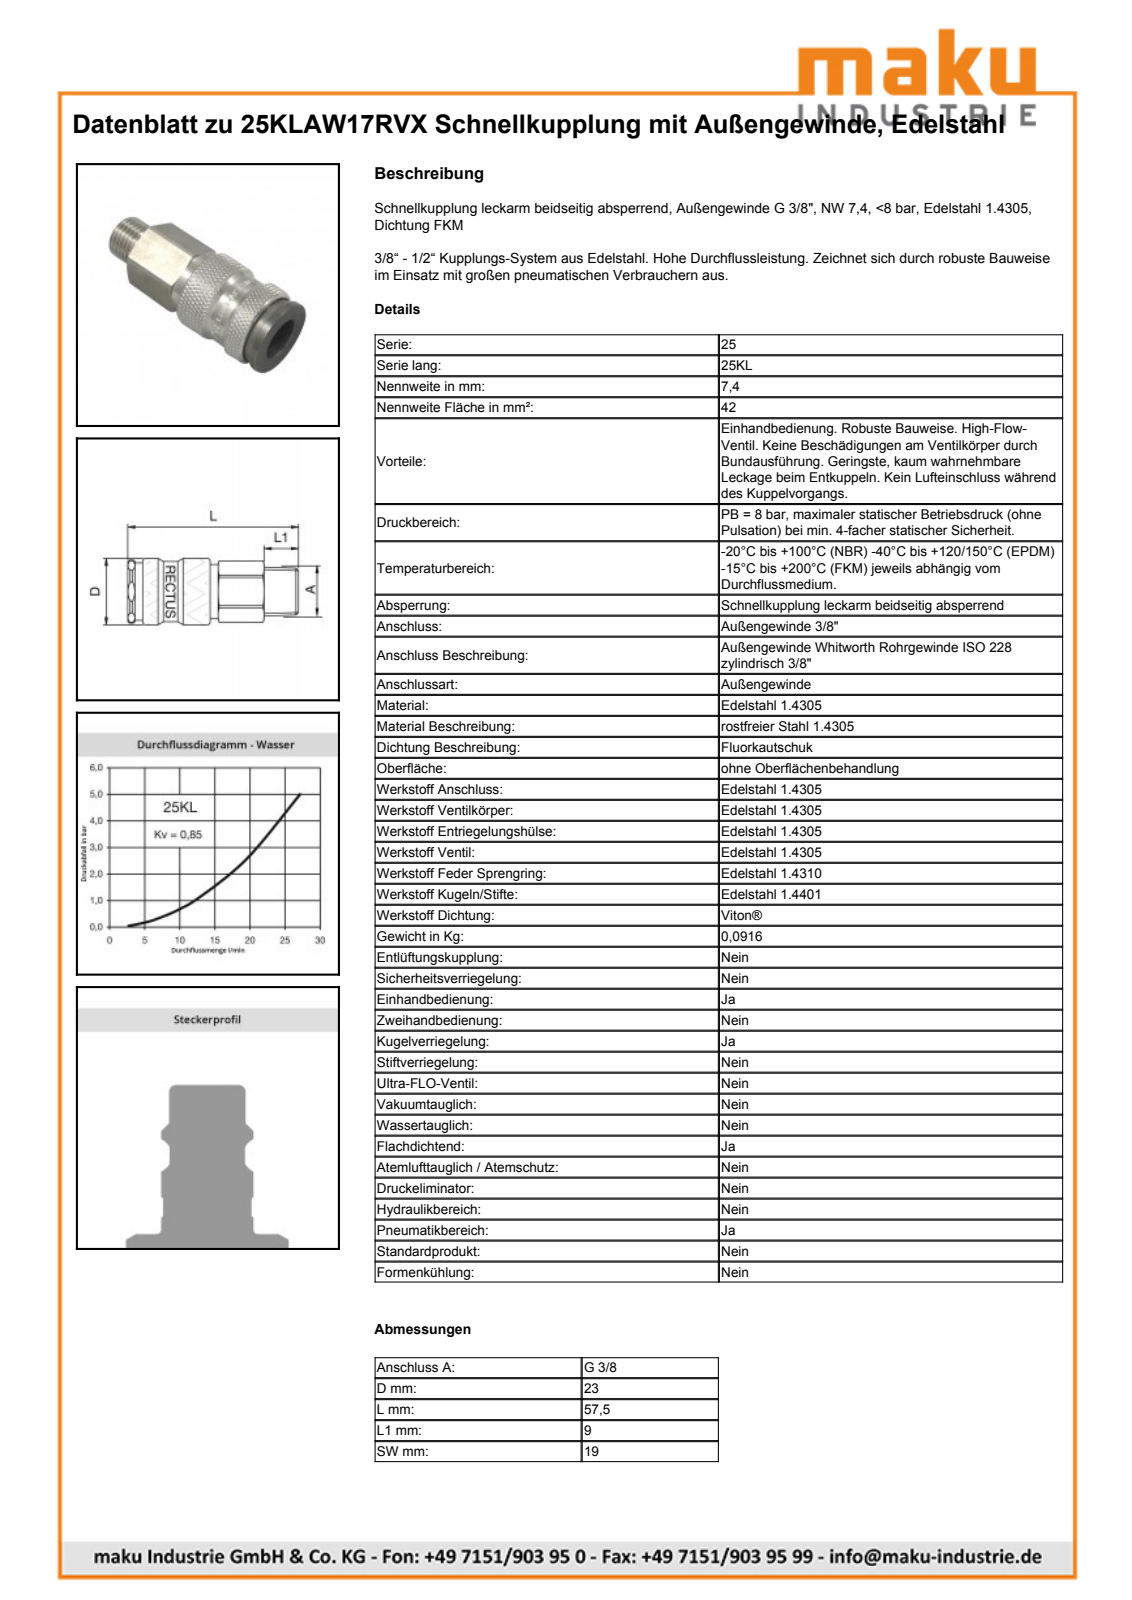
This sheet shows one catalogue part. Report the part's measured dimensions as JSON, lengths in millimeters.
{"part_name": "D112167", "step_written_by": "Autodesk Inventor 2013 (AUTOMOTIVE_DESIGN)", "units": "millimeters", "bodies": {"solids": 2, "faces": 622, "planar": 213, "cylindrical": 82, "other": 327}, "overall_size": [58.1, 23.15, 23.15], "volume_mm3": 17507, "surface_area_mm2": 9417, "round_holes": [[14, 1], [14.1, 1], [15.1, 1], [17.25, 1], [19.35, 1], [20.05, 1]], "round_bosses_or_shafts": [[23.15, 1], [21, 1], [20, 1], [18.95, 1], [16.66, 1], [16, 1], [15.3, 1]], "partial_cylinders_radius": [[10.4, 1], [10.7, 1], [11, 1]], "face_to_face_distances": [19, 58.1, 3.6, 25.1, 33, 49.1, 24, 9, 28.7, 20.4]}
